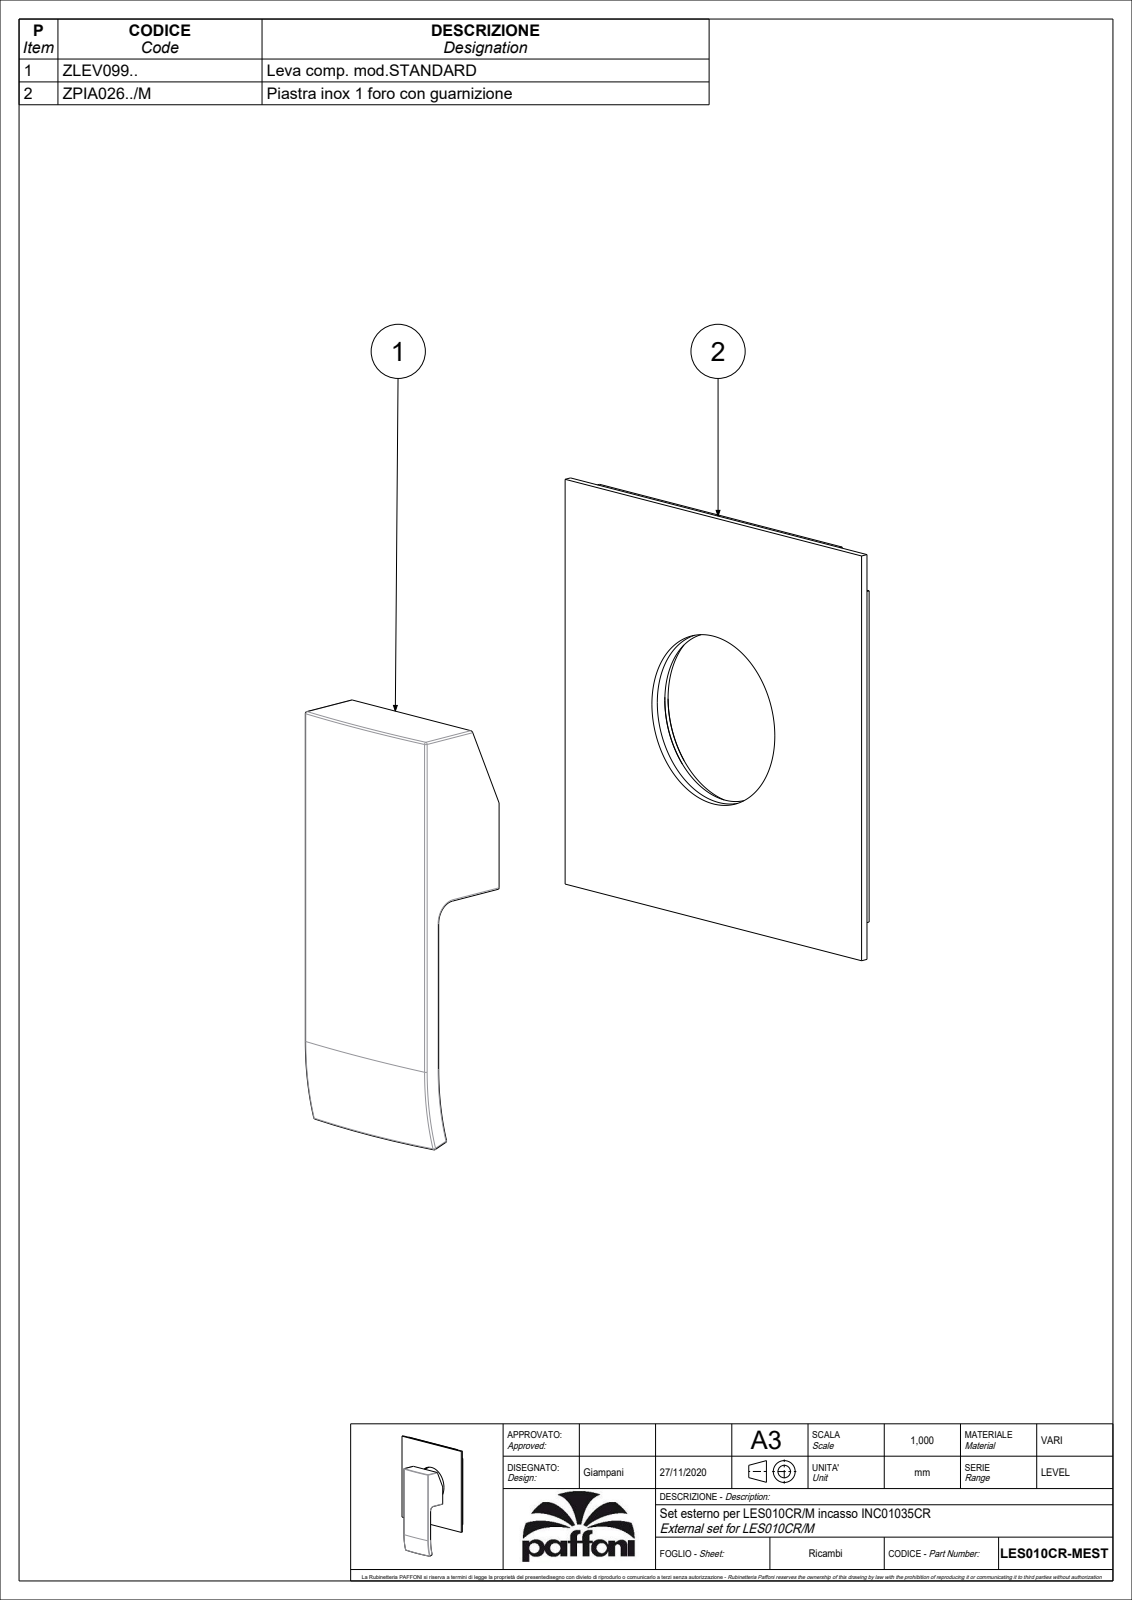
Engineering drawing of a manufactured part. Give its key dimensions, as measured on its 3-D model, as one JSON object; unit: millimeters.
{"part_name": "LES010CR-MEST", "step_written_by": "CREO PARAMETRIC BY PTC INC, 2020044 (CONFIG_CONTROL_DESIGN)", "units": "millimeters", "bodies": {"solids": 2, "faces": 187, "planar": 81, "cylindrical": 61, "other": 45}, "overall_size": [143.38, 110, 37.5], "volume_mm3": 59193, "surface_area_mm2": 45576, "round_holes": [[3, 1], [3.3, 1], [5.5, 1], [7.8, 1], [45.6, 1], [47.6, 1], [51.1, 1]], "round_bosses_or_shafts": [[54.6, 1], [7.6, 1], [5, 1]], "partial_cylinders_radius": [[1.5, 14], [0.5, 10], [2, 4], [300, 2], [2.25, 1]], "face_to_face_distances": [2, 0.8, 2.8, 45, 30, 29.2, 27.2, 32.5, 77.5, 110]}
